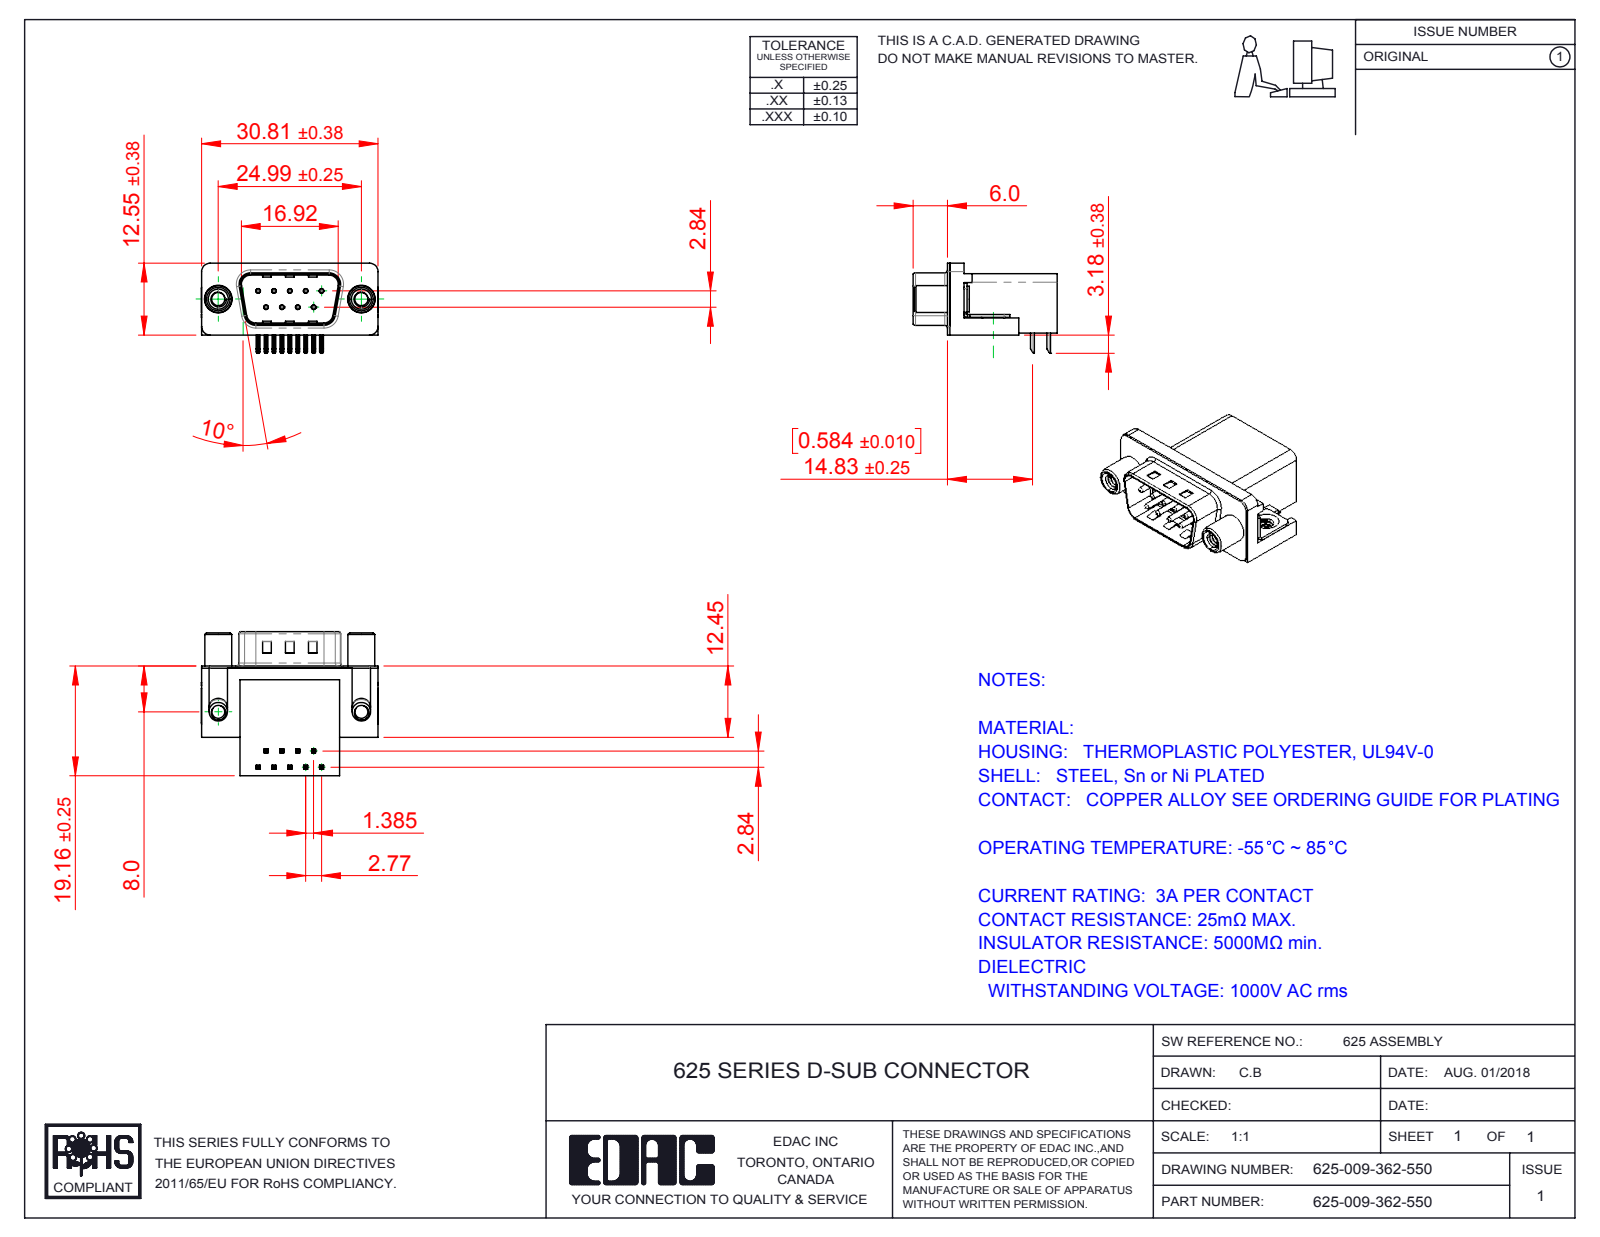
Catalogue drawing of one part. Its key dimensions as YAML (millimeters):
part_name: "625 Shell_9 Socket; 625 Contact Top; 625 Contact Bottom; 625 Housing_9 Socket (+3 more)"
step_written_by: "SolidWorks 2016 (CONFIG_CONTROL_DESIGN)"
units: millimeters
bodies: {solids: 15, faces: 1019, planar: 567, cylindrical: 337, other: 115}
overall_size: [30.89, 25.16, 15.73]
volume: 4577
surface_area: 5230
round_holes:
  - {diameter: 0.35, count: 9}
  - {diameter: 0.8, count: 9}
  - {diameter: 2.26, count: 2}
  - {diameter: 2.3, count: 2}
  - {diameter: 3.1, count: 2}
  - {diameter: 4, count: 2}
  - {diameter: 4.8, count: 2}
  - {diameter: 5, count: 2}
round_bosses_or_shafts:
  - {diameter: 0.75, count: 9}
  - {diameter: 4.9, count: 2}
  - {diameter: 4.7, count: 2}
  - {diameter: 4.5, count: 2}
  - {diameter: 3.85, count: 2}
  - {diameter: 3.26, count: 2}
partial_cylinders:
  - {radius: 0.25, count: 36}
  - {radius: 0.12, count: 18}
  - {radius: 1, count: 16}
  - {radius: 0.5, count: 9}
  - {radius: 1.5, count: 8}
  - {radius: 1.6, count: 8}
  - {radius: 0.9, count: 4}
  - {radius: 2, count: 4}
face_to_face_distances: [0.4, 10.34, 18.76, 19.16, 16.26, 2.5, 2.9, 0.35, 10.69, 6.7]
hole_center_spacings: [3.16, 2.77, 5.54, 5.03, 5.04, 8.31, 7.48, 7.49]
